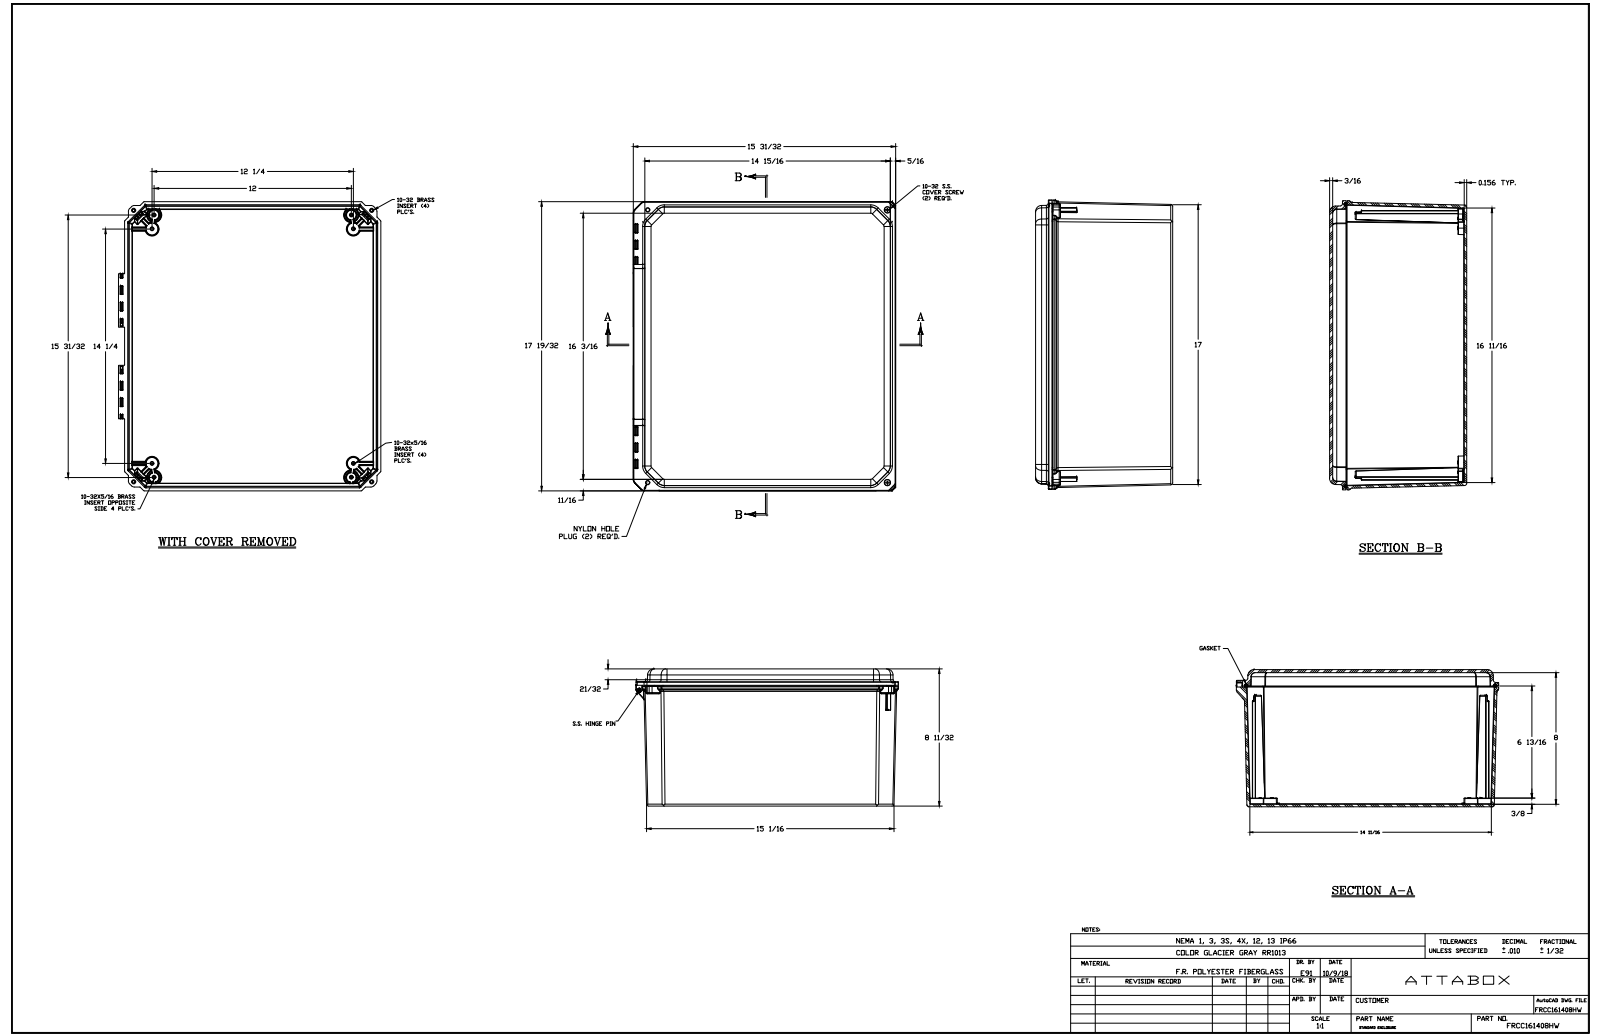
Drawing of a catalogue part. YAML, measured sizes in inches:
part_name: "FRCC161408HW"
step_written_by: "SolidWorks 2018 (AUTOMOTIVE_DESIGN)"
units: inches
bodies: {solids: 23, faces: 2108, planar: 592, cylindrical: 800, other: 716}
overall_size: [17.591, 15.965, 8.341]
volume: 171.6
surface_area: 2183
round_holes:
  - {diameter: 0.156, count: 12}
  - {diameter: 0.152, count: 8}
  - {diameter: 0.219, count: 4}
  - {diameter: 0.252, count: 4}
  - {diameter: 0.312, count: 4}
  - {diameter: 0.137, count: 2}
  - {diameter: 0.15, count: 2}
round_bosses_or_shafts:
  - {diameter: 0.246, count: 12}
  - {diameter: 0.45, count: 2}
  - {diameter: 0.209, count: 2}
  - {diameter: 0.199, count: 2}
  - {diameter: 0.135, count: 1}
  - {diameter: 0.135, count: 1}
partial_cylinders:
  - {radius: 0.01, count: 202}
  - {radius: 0.005, count: 116}
  - {radius: 0.02, count: 59}
  - {radius: 0.03, count: 39}
  - {radius: 0.125, count: 29}
  - {radius: 0.03, count: 24}
  - {radius: 0.09, count: 24}
  - {radius: 0.25, count: 24}
face_to_face_distances: [0.125, 0.156, 8.216, 8.06, 8.341, 8.185, 0.18, 0.181, 7.281, 7.125]
hole_center_spacings: [19.37, 0.865, 1.33, 1.651, 12.156, 12.25, 13.296, 13.469]
